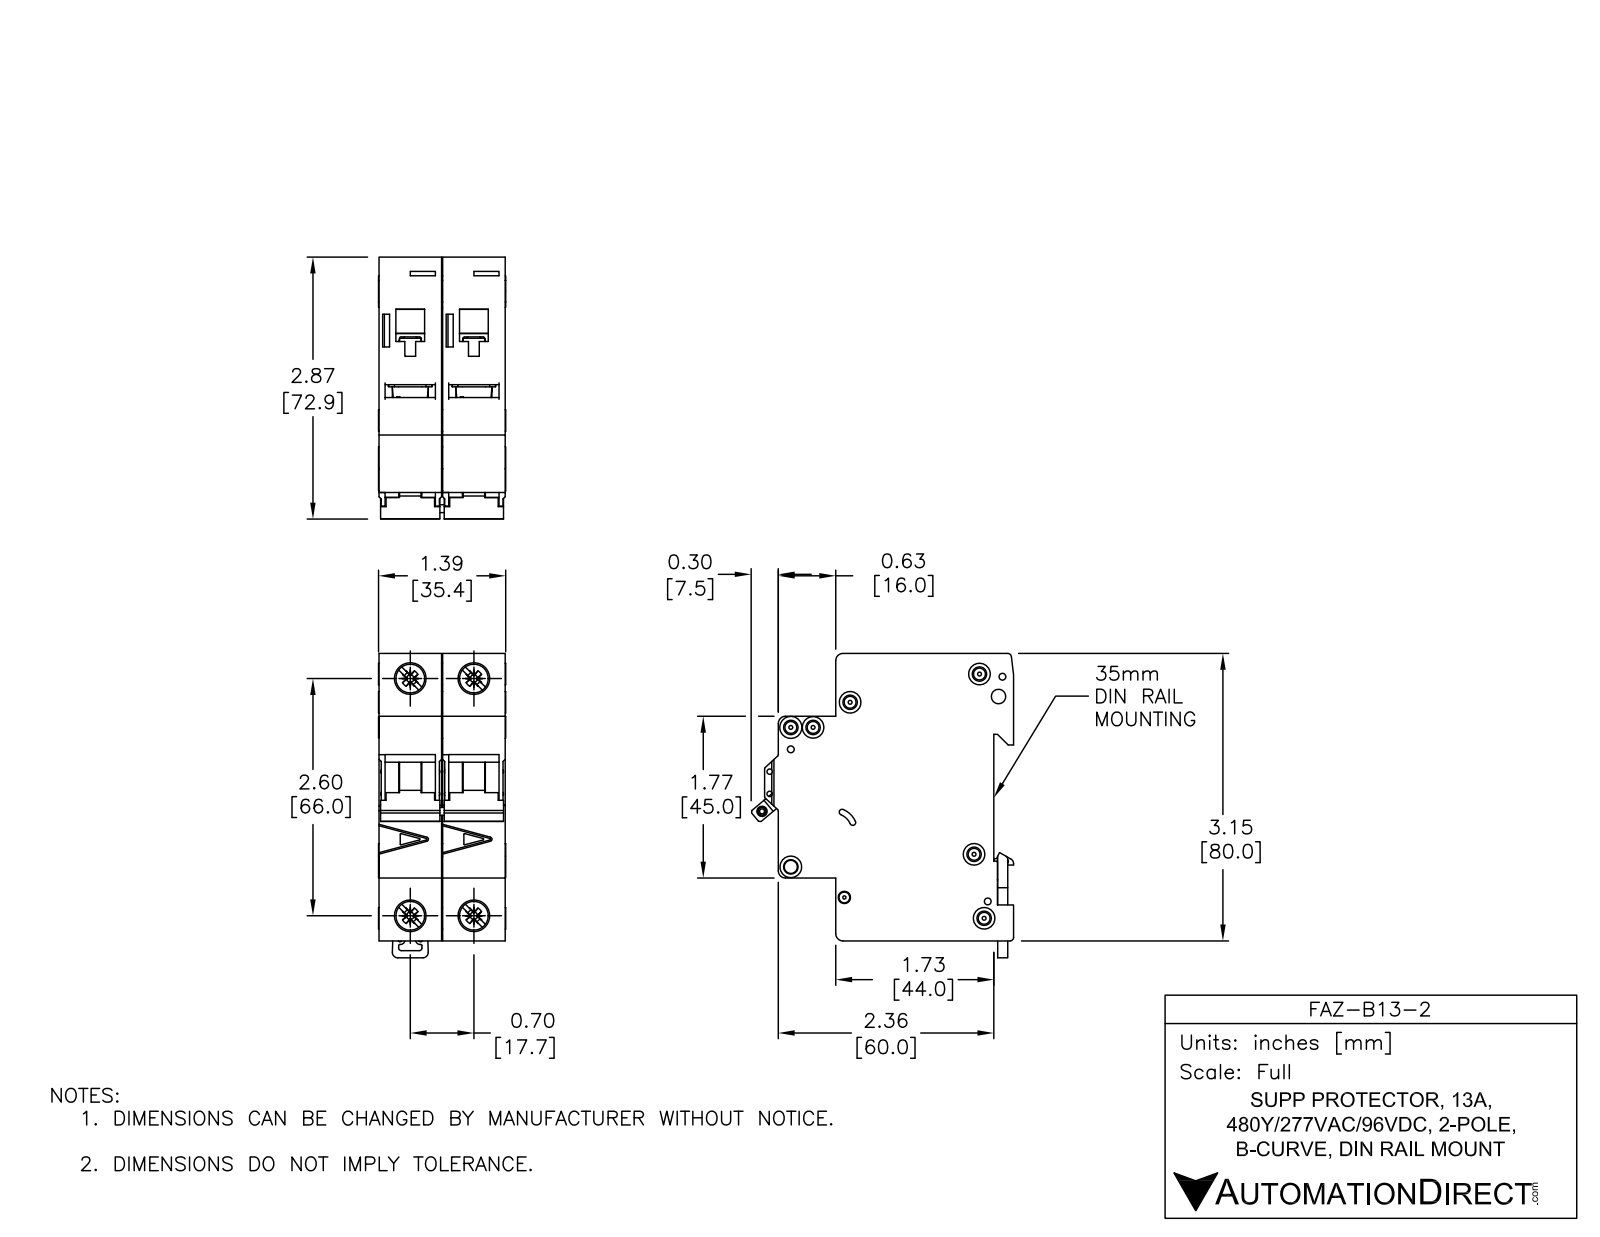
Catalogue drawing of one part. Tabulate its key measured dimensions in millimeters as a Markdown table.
| quantity | value |
| --- | --- |
| part name | FAZ-B13-2 |
| STEP written by | SolidWorks 2014 (AUTOMOTIVE_DESIGN) |
| units | millimeters |
| bodies | 8 solids, 1104 faces (466 planar, 396 cylindrical, 242 other) |
| overall size | 84.78 × 73.04 × 35.4 |
| volume | 149 808 mm³ |
| surface area | 38 799 mm² |
| round holes (diameter × count) | 3.6 × 6, 1.9 × 3, 1.09 × 2, 1.5 × 2, 4 × 2, 7.15 × 2, 8.2 × 2, 2.15 × 1, 2.2 × 1, 2.55 × 1, 3.3 × 1, 3.4 × 1 |
| round bosses / shafts (diameter × count) | 6 × 4, 8.2 × 2, 2.5 × 2 |
| partial cylindrical surfaces (radius × count) | 0.25 × 49, 0.5 × 19, 2 × 10, 0.2 × 8, 1 × 8, 0.8 × 2, 1.8 × 2, 3 × 2 |
| main face-to-face distances | 17.7, 17.5, 35.2, 79.48, 5.5, 49.5, 44, 65.5, 60, 16 |
| hole center spacings | 6.2, 13.64, 17.7, 66, 68.33, 4.81, 5.19, 5.61 |
